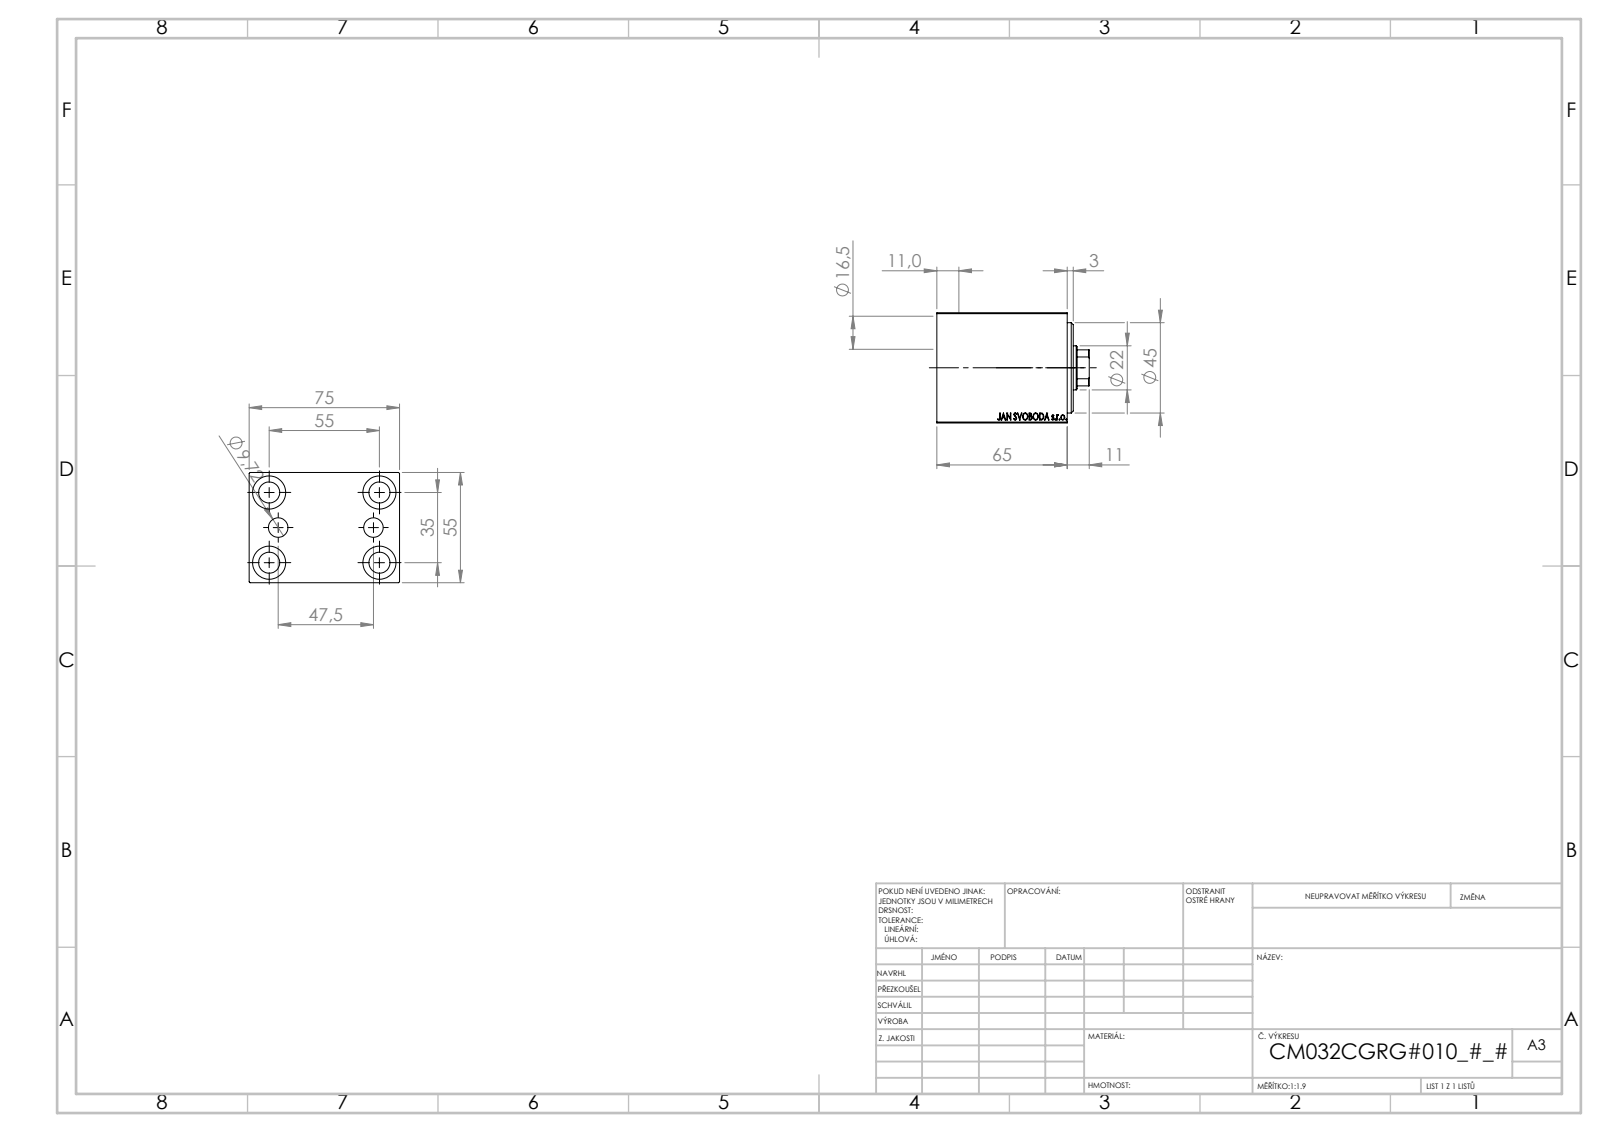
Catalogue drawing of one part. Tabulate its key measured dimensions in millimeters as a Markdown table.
| quantity | value |
| --- | --- |
| part name | V450CM_C_Body; V450CM_VC_B; V450CM_C_VCP |
| STEP written by | SolidWorks 2019 (CONFIG_CONTROL_DESIGN) |
| units | millimeters |
| bodies | 3 solids, 858 faces (408 planar, 56 cylindrical, 394 other) |
| overall size | 77 × 75 × 55 |
| volume | 233 193 mm³ |
| surface area | 50 806 mm² |
| round holes (diameter × count) | 10.5 × 5, 16.5 × 4, 4 × 2, 9.72 × 2, 22 × 1, 25.5 × 1, 32 × 1, 34 × 1, 45 × 1 |
| partial cylindrical surfaces (radius × count) | 10.5 × 1 |
| main face-to-face distances | 55, 75, 5, 31.25, 65, 33.75, 60, 28.75, 10, 11 |
| hole center spacings | 17.9, 32.6, 54.16, 23.75, 35, 55, 65.19, 47.5 |
